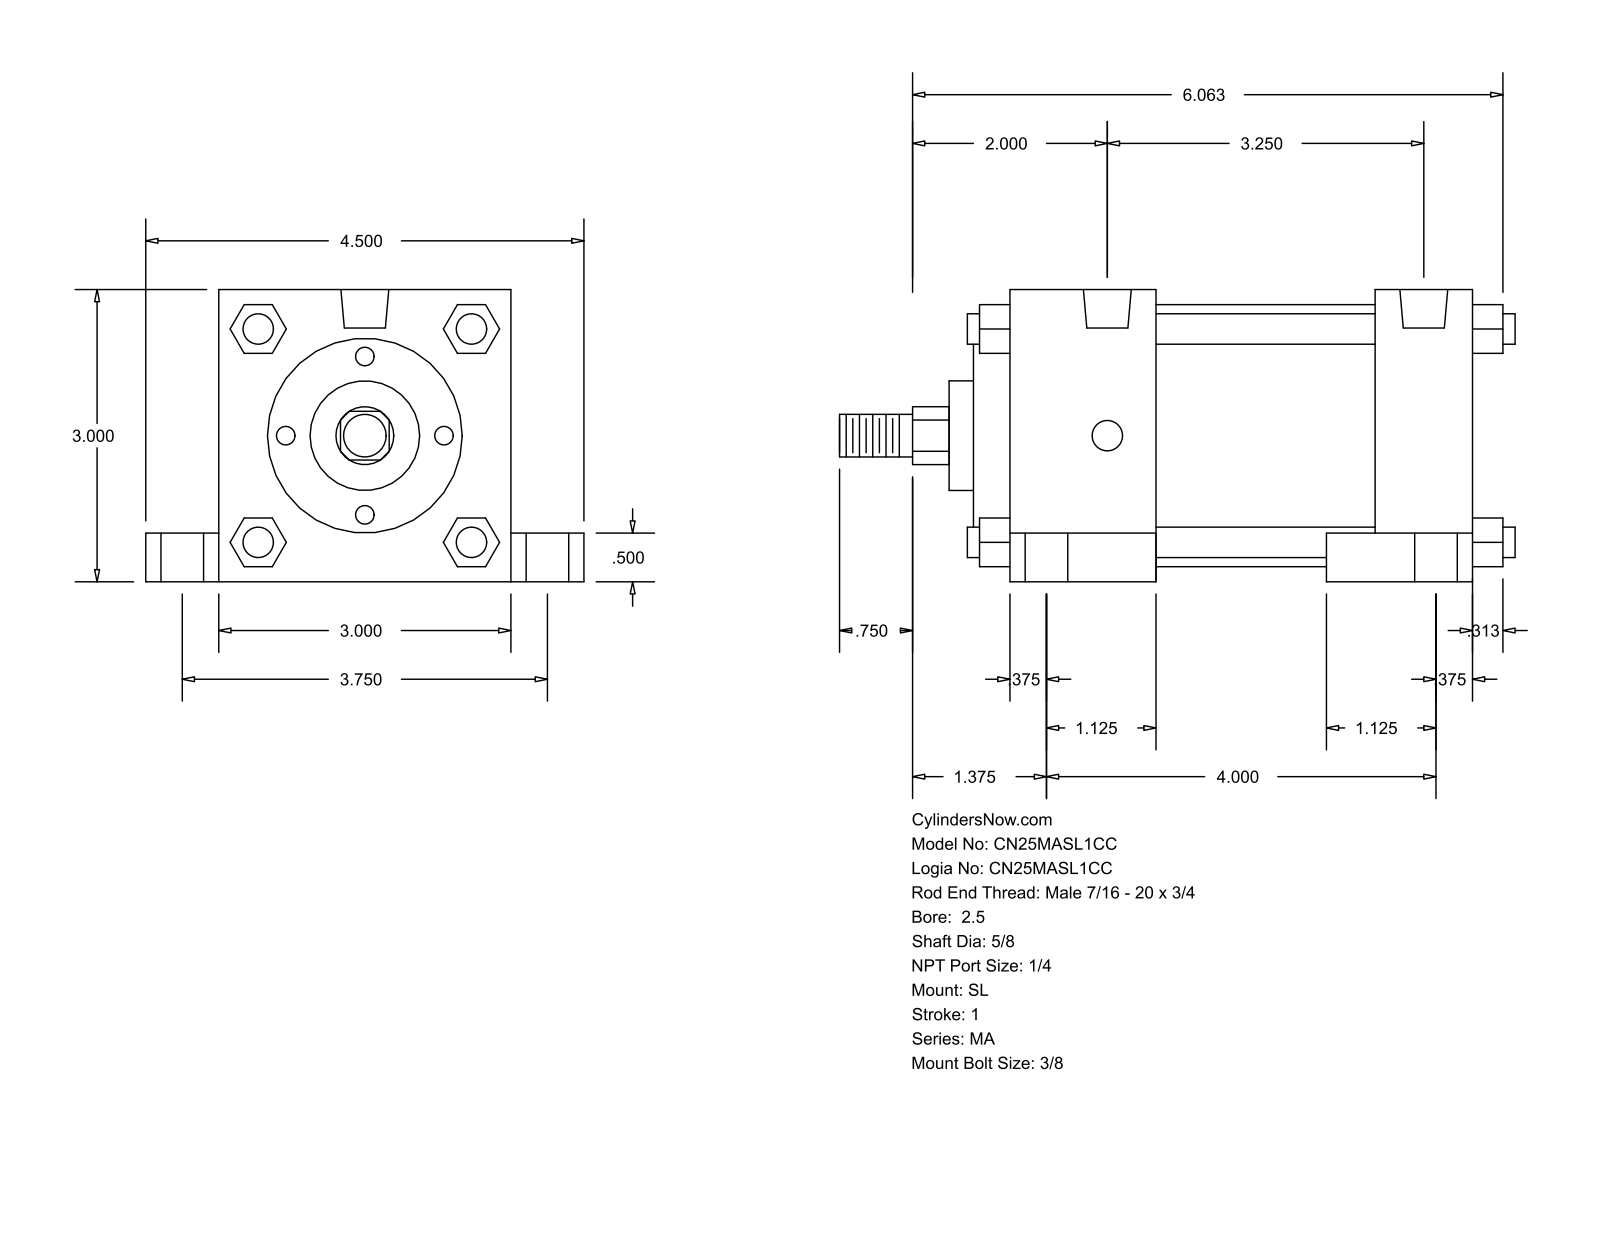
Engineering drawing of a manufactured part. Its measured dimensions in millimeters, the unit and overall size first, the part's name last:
Units: millimetres
Overall size (bounding box): 176.21 × 114.3 × 76.2
Round holes (diameter × count): ⌀7.94 ×4, ⌀11.11 ×4, ⌀17.46 ×4, ⌀12.49 ×2
Round bosses / shafts (diameter × count): ⌀7.94 ×4, ⌀68.33 ×1, ⌀50.8 ×1, ⌀28.57 ×1, ⌀15.88 ×1, ⌀11.11 ×1
Partial cylindrical surfaces — rounded edges, fillets, slot ends (radius × count): R7.54 ×1
Main face-to-face distances: 76.2, 95.25, 120.65, 12.7, 57.15, 25.4, 82.55, 38.1, 19.05, 63.5
Hole centre spacings: 47.73, 50.2, 82.55, 95.24, 98.07, 101.61, 109.34, 139.27
Bodies: 0 solids, 150 faces (113 planar, 37 cylindrical, 0 other)
Part name (STEP PRODUCT): MA_SL__0250_0.625
STEP written by: GSSL Pune (CONFIG_CONTROL_DESIGN)
